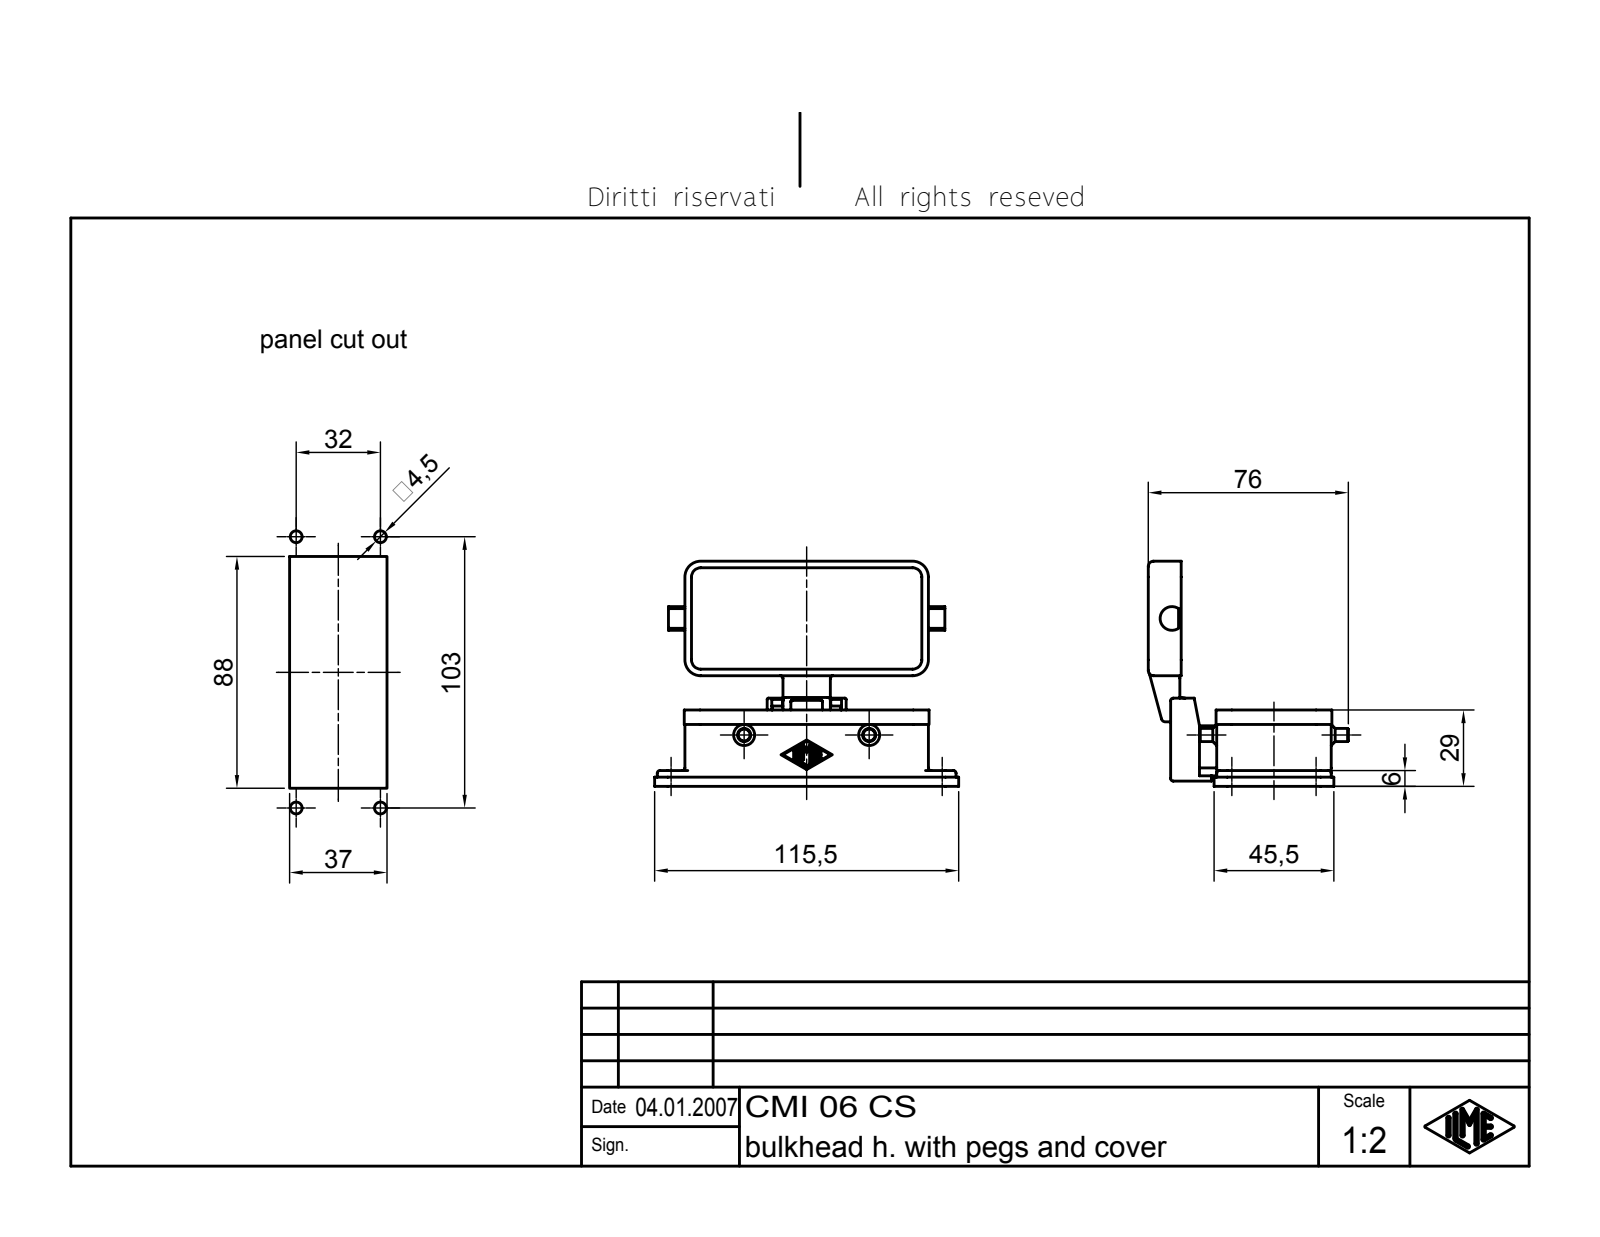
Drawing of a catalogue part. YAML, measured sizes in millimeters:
part_name: "CMI 06 CS"
step_written_by: "Autodesk Inventor 7 (AUTOMOTIVE_DESIGN)"
units: millimeters
bodies: {solids: 2, faces: 471, planar: 183, cylindrical: 192, other: 96}
overall_size: [115.5, 85.5, 76]
volume: 63191
surface_area: 40463
round_holes:
  - {diameter: 4.5, count: 4}
  - {diameter: 4.6, count: 4}
  - {diameter: 4, count: 1}
  - {diameter: 5, count: 1}
round_bosses_or_shafts:
  - {diameter: 5, count: 2}
  - {diameter: 3, count: 2}
  - {diameter: 7, count: 1}
  - {diameter: 4, count: 1}
partial_cylinders:
  - {radius: 1, count: 20}
  - {radius: 0.38, count: 14}
  - {radius: 6, count: 12}
  - {radius: 0.5, count: 9}
  - {radius: 0.7, count: 8}
  - {radius: 2, count: 8}
  - {radius: 3.5, count: 8}
  - {radius: 2.5, count: 4}
face_to_face_distances: [3, 3.5, 40.5, 4, 2.5, 29, 25.5, 43.5, 0.75, 38.5]
hole_center_spacings: [32, 103, 107.86]
